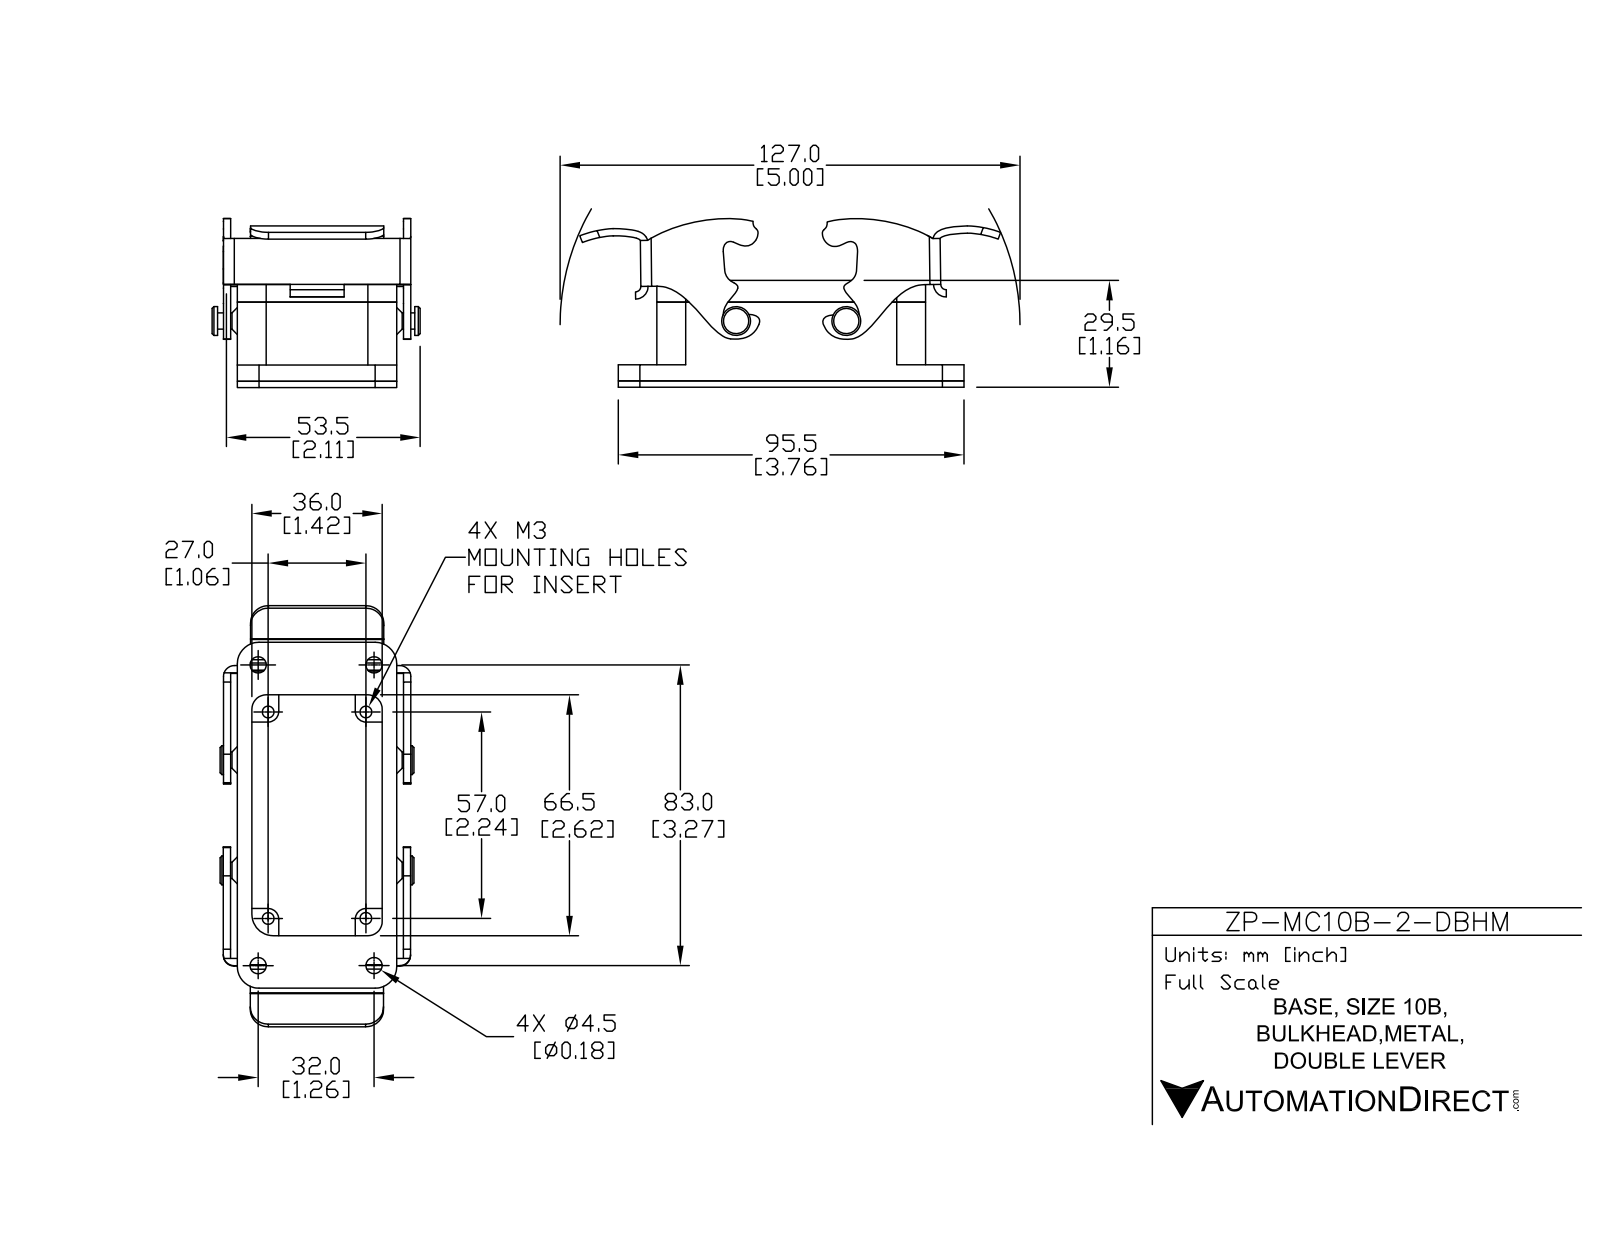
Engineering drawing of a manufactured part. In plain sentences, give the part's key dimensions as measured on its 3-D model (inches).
The part is named "ZP-MC10B-2-DBHM". Its 3-D file was written by "SolidWorks 2021 (CONFIG_CONTROL_DESIGN)". It is 5 solids with 350 faces: 118 planar, 216 cylindrical and 16 other. Overall it measures 5.004 by 2.274 by 1.729 inches. Its volume is 2.13 cubic inches and its surface area 52.67 square inches. Round holes: 4 of diameter 0.128, 4 of diameter 0.177. Round bosses or shafts: 2 of diameter 0.315, 2 of diameter 0.177. Partial cylindrical surfaces (rounded edges, fillets, slot ends): 30 of radius 0.02, 9 of radius 0.157, 6 of radius 0.079, 6 of radius 0.118, 6 of radius 0.236, 4 of radius 0.039, 4 of radius 0.315, 4 of radius 0.394. The main face-to-face distances are 0.045, 0.237, 1.713, 1.905, 0.192, 1.668, 0.133, 1.609, 1.476, 0.069. The hole center spacings are 1.063, 1.26, 2.244, 2.483, 3.268, 3.502, 0.501, 0.505.
